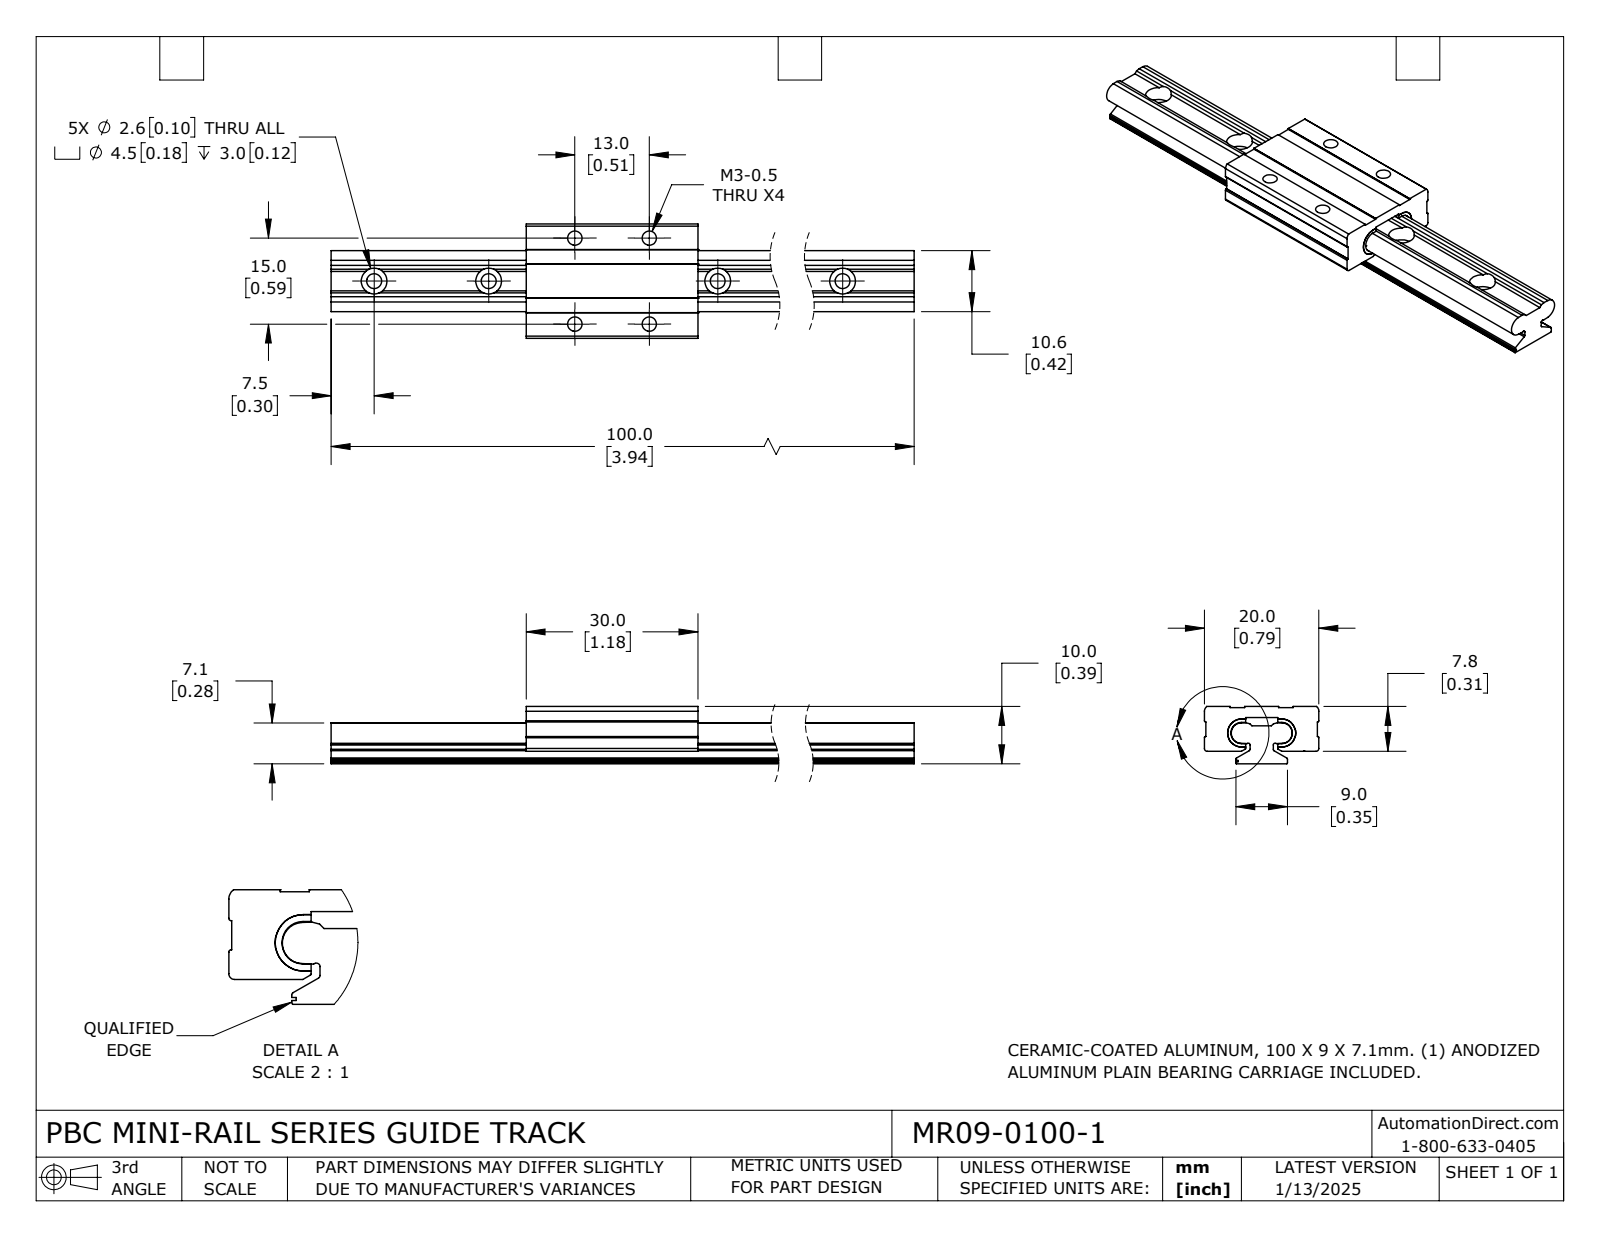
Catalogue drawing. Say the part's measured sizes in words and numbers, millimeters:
The part is named "MR09-0100-1_RAIL; MR09-0100-1; MR09-0100-1_CARRIAGE". Its 3-D file was written by "SolidWorks 2023 (CONFIG_CONTROL_DESIGN)". It is 4 solids with 166 faces: 103 planar, 63 cylindrical and 0 other. Overall it measures 100 by 20 by 10 millimeters. Its volume is 8 260 cubic millimeters and its surface area 8 252 square millimeters. Round holes: 5 of diameter 2.6, 5 of diameter 4.5, 4 of diameter 2.5. Partial cylindrical surfaces (rounded edges, fillets, slot ends): 10 of radius 0.2, 6 of radius 0.3, 4 of radius 1.9, 2 of radius 0.3, 2 of radius 0.5, 2 of radius 1, 2 of radius 1.8, 2 of radius 2.5. The main face-to-face distances are 10, 2.2, 7.8, 6.6, 4.4, 3.4, 3.9, 5.9, 8.1, 1.5. The hole center spacings are 20, 40, 9, 11, 13, 14.1, 15, 16.8.
